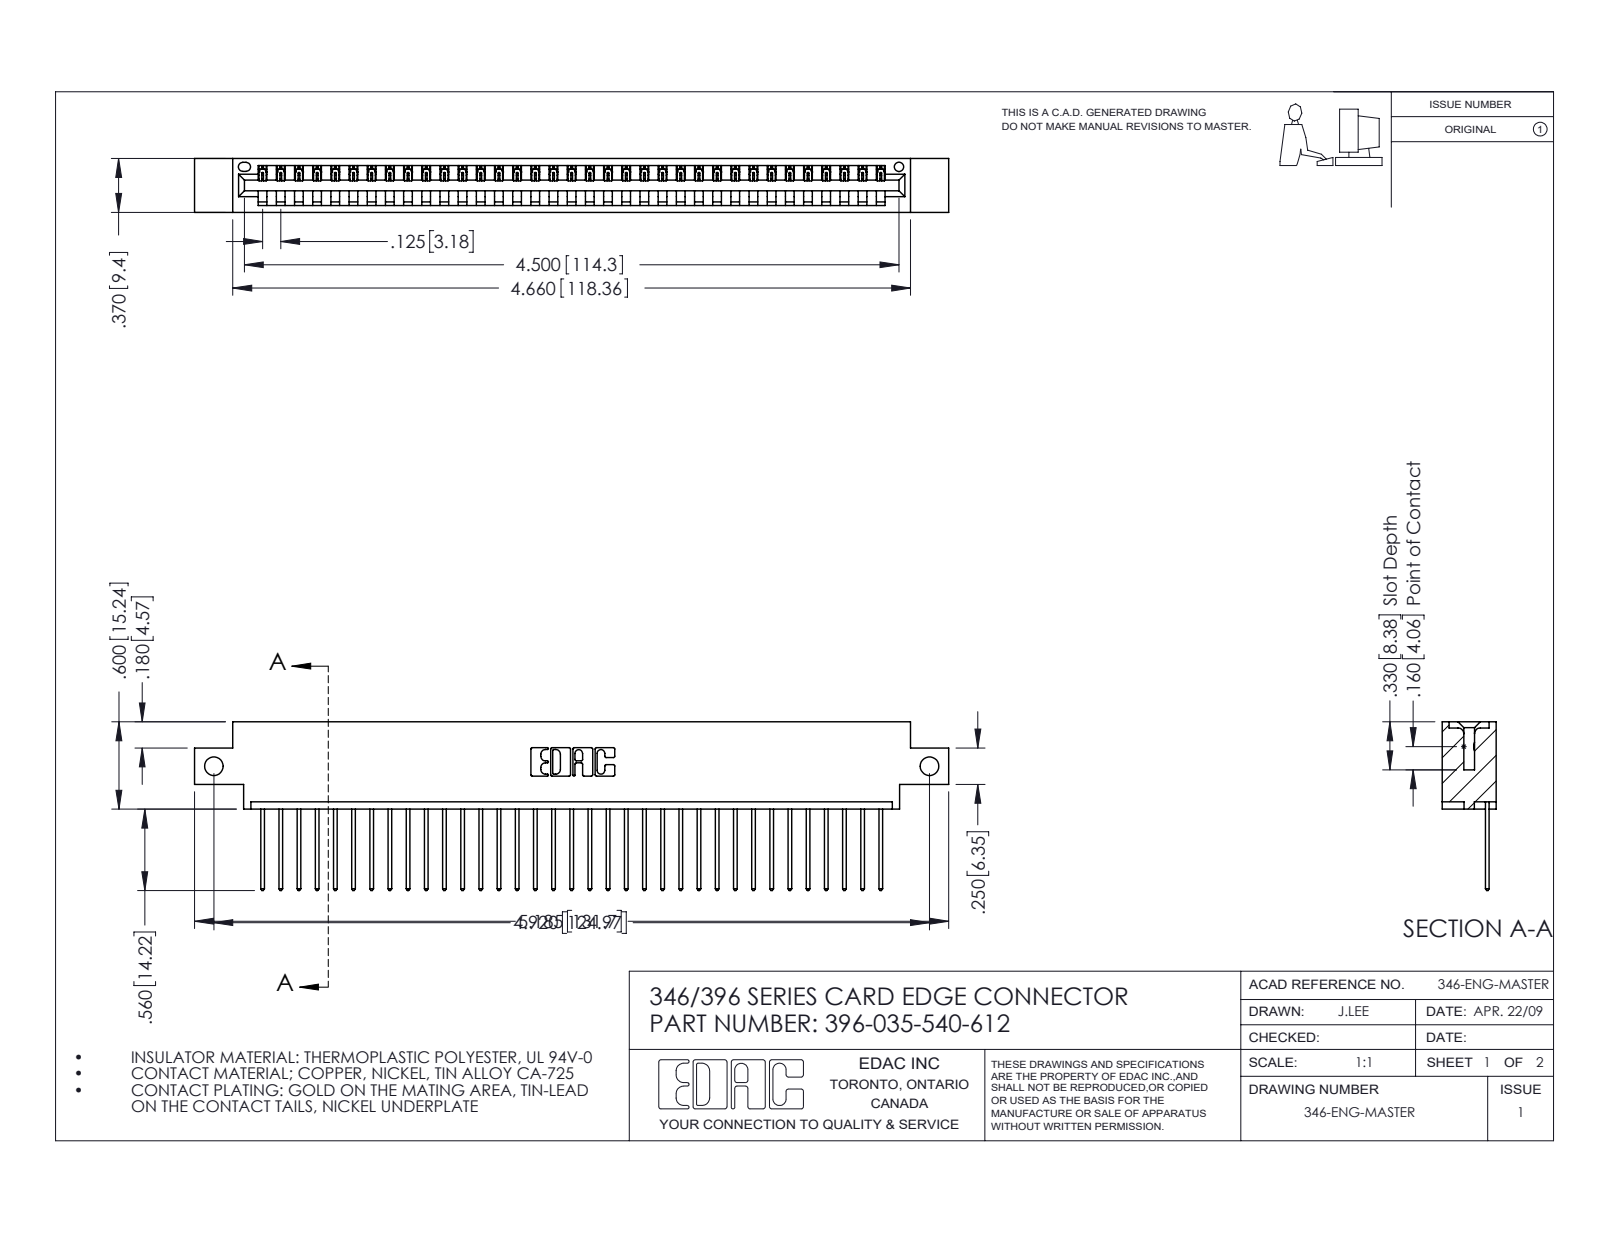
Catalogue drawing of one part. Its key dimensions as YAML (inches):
part_name: "345-292-001_345-293-140; 396-035-540-612; 346 Part_0.170 Offset - Side Mount"
step_written_by: "SolidWorks 2016 (CONFIG_CONTROL_DESIGN)"
units: inches
bodies: {solids: 36, faces: 2156, planar: 1480, cylindrical: 676, other: 0}
overall_size: [5.185, 1.16, 0.37]
volume: 0.754
surface_area: 24.39
round_holes:
  - {diameter: 0.128, count: 2}
  - {diameter: 0.064, count: 1}
partial_cylinders:
  - {radius: 0.006, count: 70}
  - {radius: 0.01, count: 70}
  - {radius: 0.01, count: 22}
  - {radius: 0.007, count: 6}
  - {radius: 0.031, count: 6}
  - {radius: 0.026, count: 3}
  - {radius: 0.031, count: 2}
  - {radius: 0.04, count: 2}
face_to_face_distances: [0.048, 0.322, 0.37, 0.25, 0.072, 0.298, 0.025, 0.148, 0.222, 0.1]
hole_center_spacings: [4.92]
